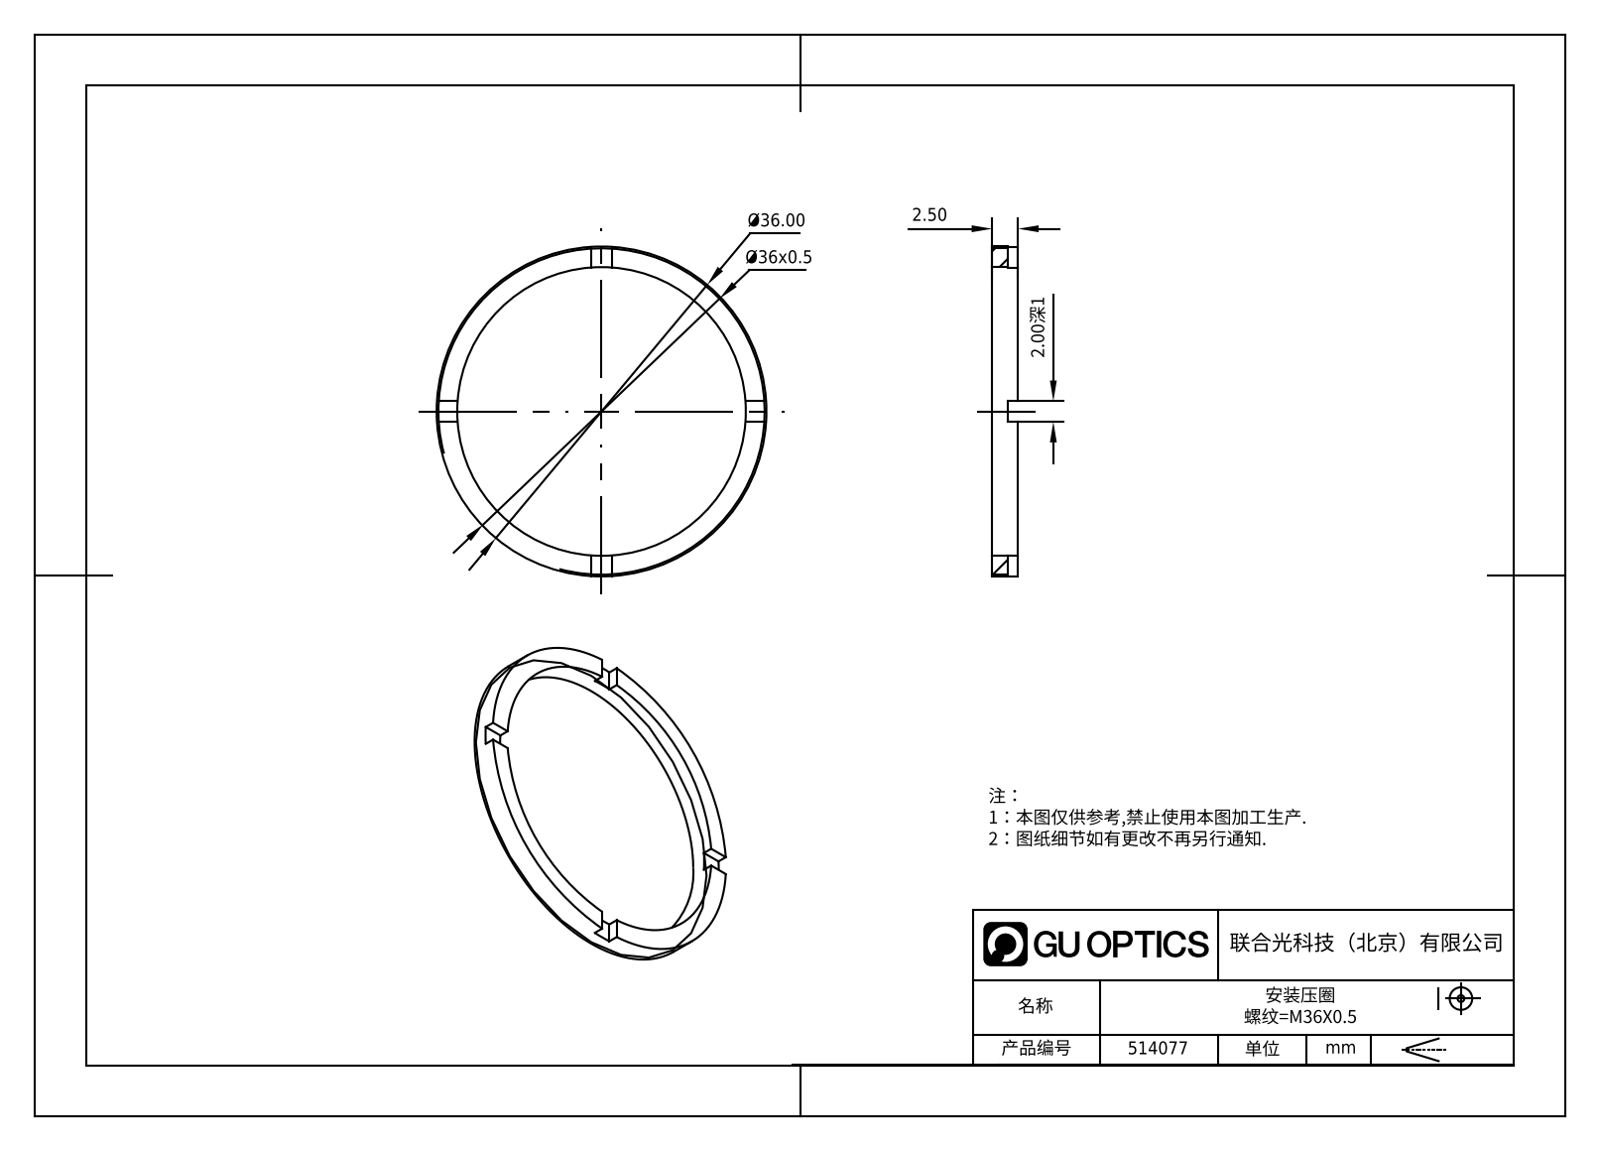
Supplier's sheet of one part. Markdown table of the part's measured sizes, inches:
| quantity | value |
| --- | --- |
| part name | 514077 |
| STEP written by | SolidWorks 2020 (CONFIG_CONTROL_DESIGN) |
| units | inches |
| bodies | 1 solid, 21 faces (17 planar, 4 cylindrical, 0 other) |
| overall size | 1.417 × 1.417 × 0.098 |
| volume | 0.032 in³ |
| surface area | 1.49 in² |
| round holes (diameter × count) | 1.26 × 1 |
| round bosses / shafts (diameter × count) | 1.417 × 1 |
| main face-to-face distances | 0.098, 0.059, 0.039, 0.079 |
